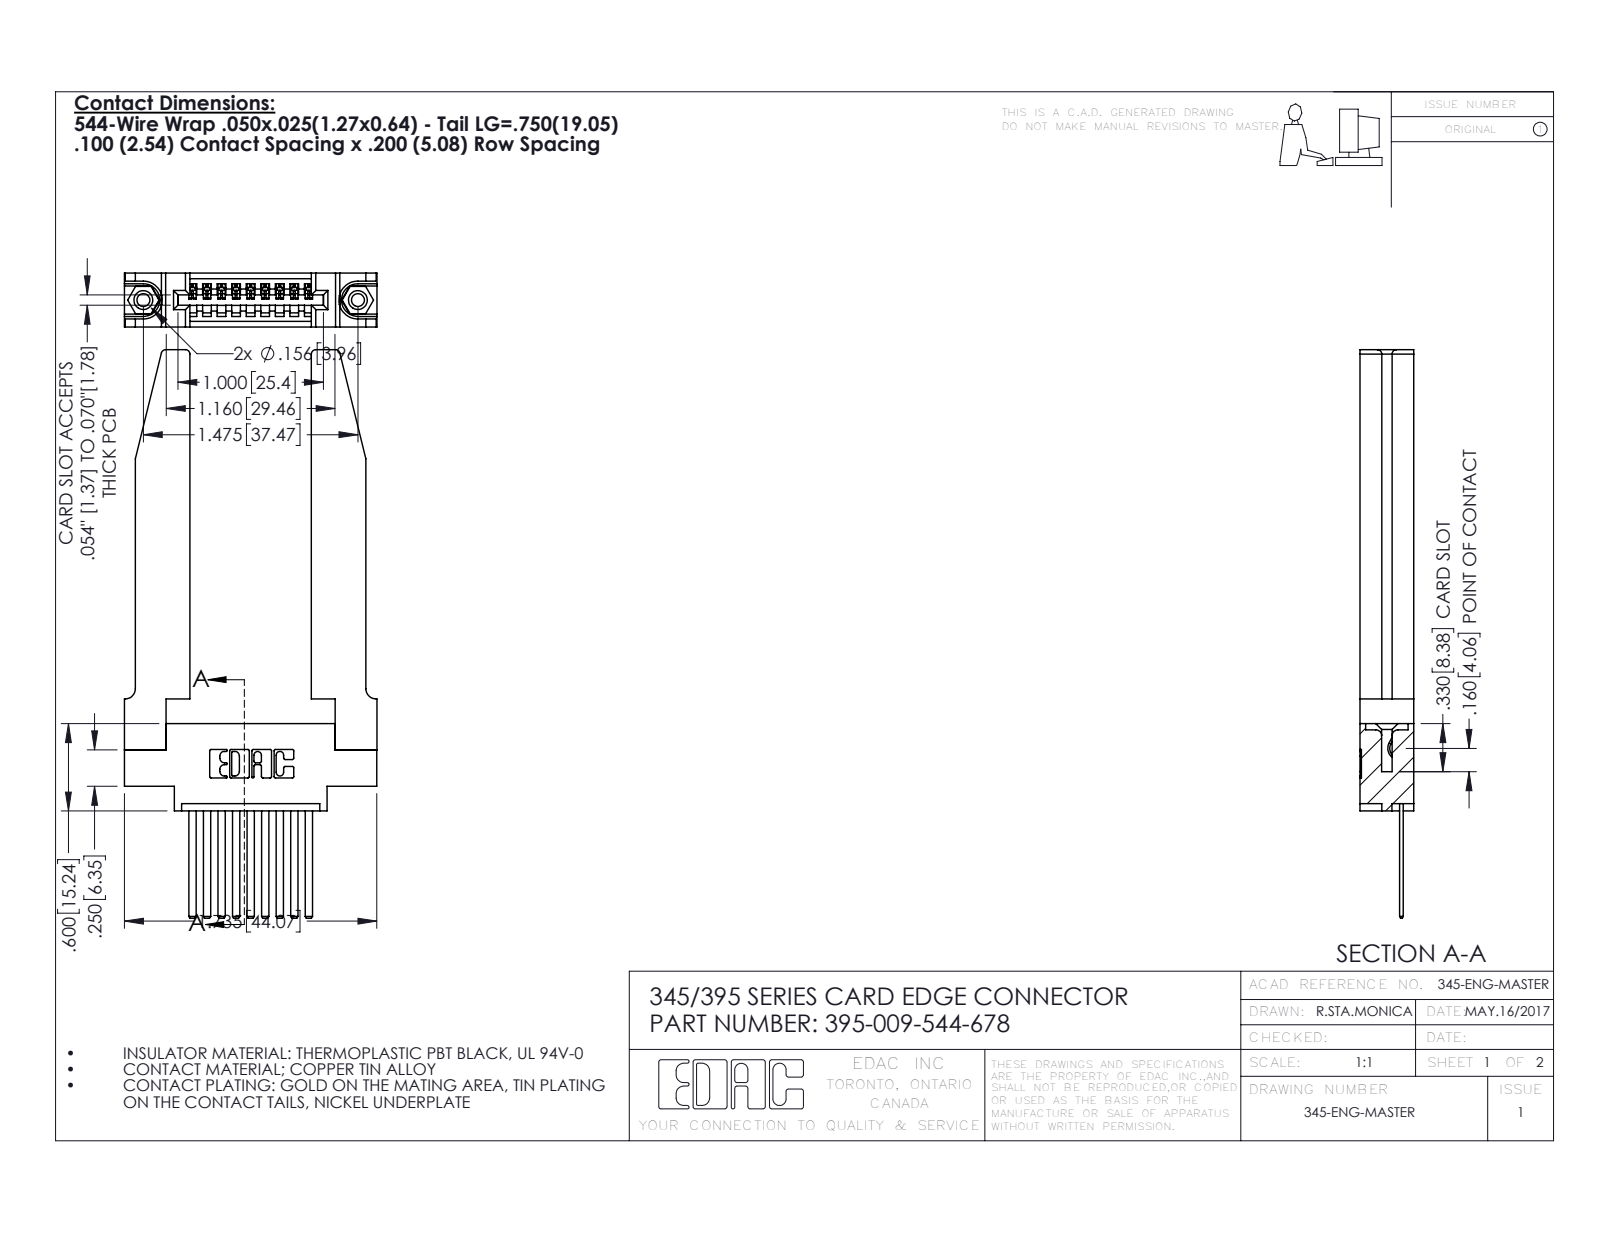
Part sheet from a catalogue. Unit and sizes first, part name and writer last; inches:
Units: inches
Overall size (bounding box): 3.907 × 1.736 × 0.37
Round holes (diameter × count): ⌀0.089 ×2, ⌀0.125 ×2, ⌀0.156 ×2, ⌀0.064 ×1
Round bosses / shafts (diameter × count): ⌀0.155 ×2
Partial cylindrical surfaces — rounded edges, fillets, slot ends (radius × count): R0.01 ×22, R0.006 ×18, R0.03 ×8, R0.007 ×6, R0.031 ×6, R0.026 ×3, R0.031 ×2, R0.04 ×2
Main face-to-face distances: 0.37, 0.072, 0.298, 0.15, 0.148, 0.22, 0.098, 0.272, 0.025, 0.077
Hole centre spacings: 0.27, 1.244, 1.475
Volume: 0.713 in³ · Surface area: 18.65 in²
Bodies: 14 solids, 832 faces (550 planar, 230 cylindrical, 52 other)
Part name (STEP PRODUCT): 345-292-001_345-293-144; 345-220-078_345-220-078; 345-250-001_345-250-001-102; 395-009-544-678 (+1 more)
STEP written by: SolidWorks 2016 (CONFIG_CONTROL_DESIGN)
